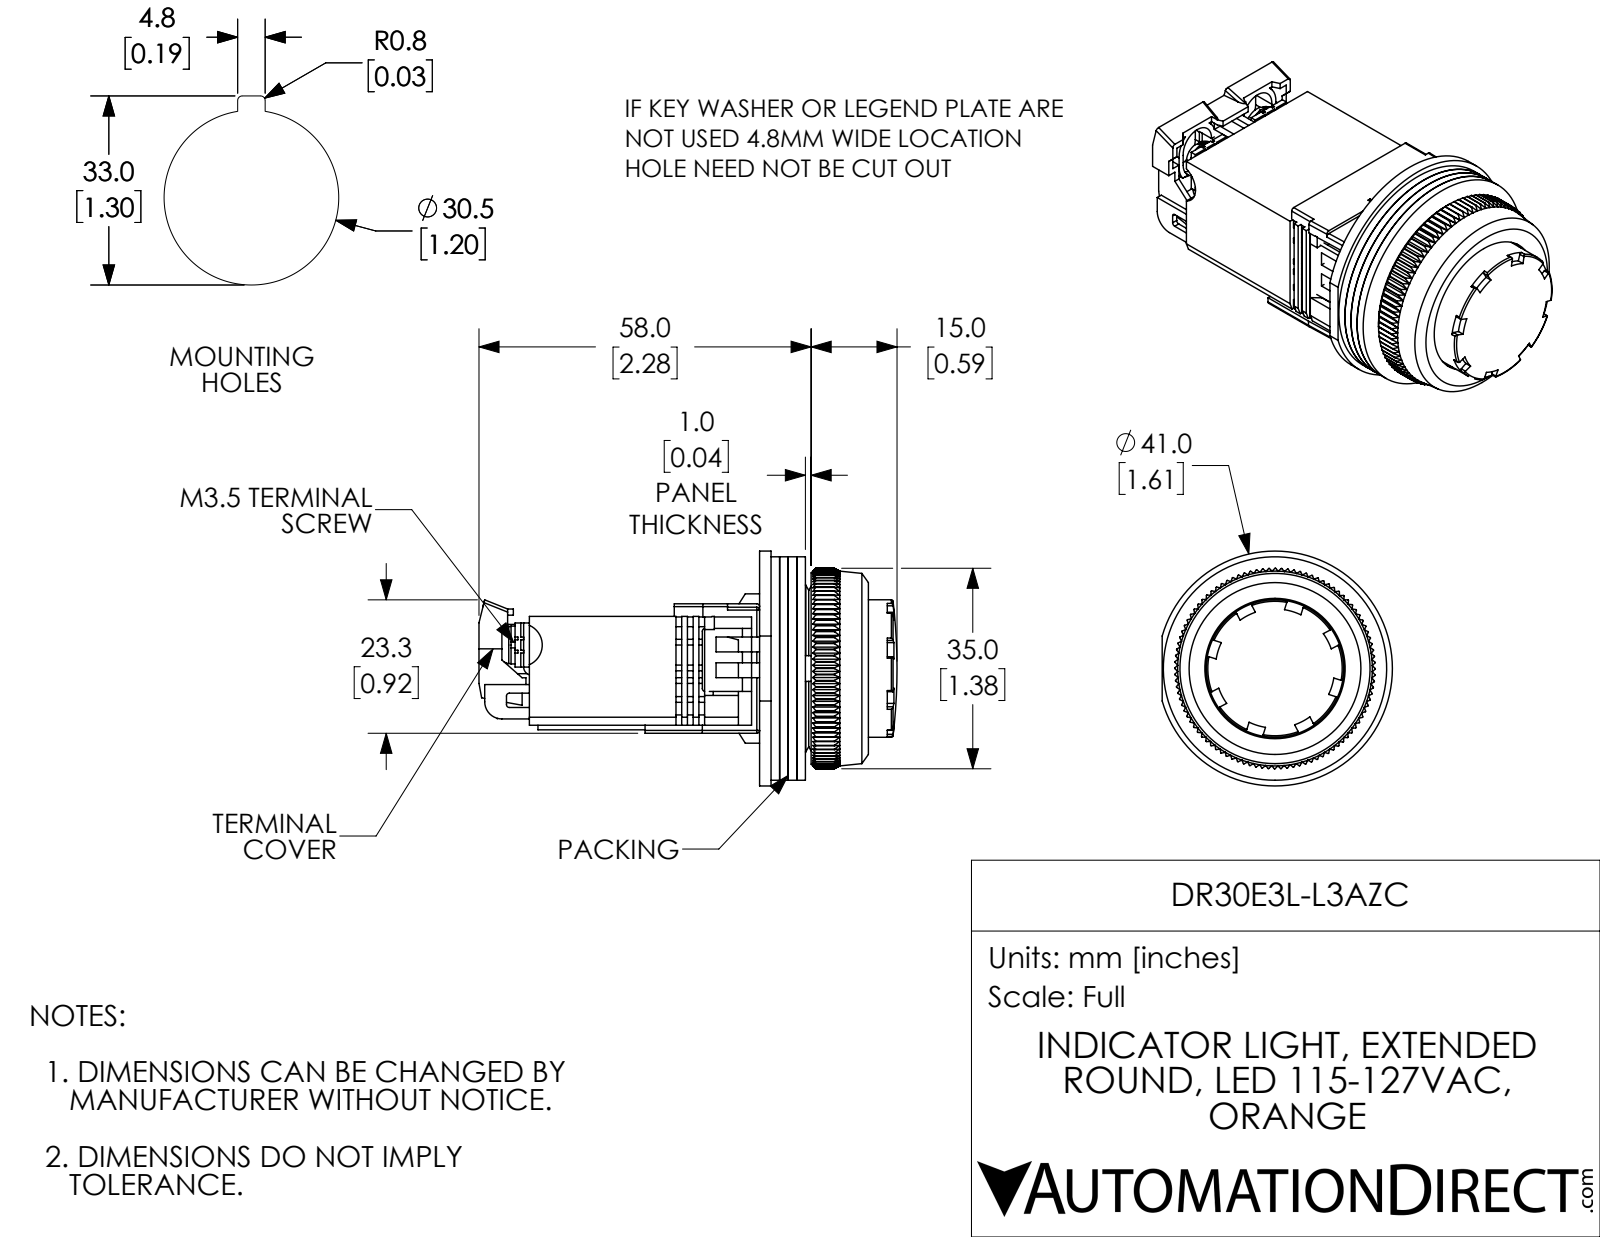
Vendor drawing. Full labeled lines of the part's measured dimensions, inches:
Part name (STEP PRODUCT): DR30E3L-L3AZC
STEP written by: SolidWorks 2017 (AUTOMOTIVE_DESIGN)
Units: inches
Bodies: 19 solids, 1662 faces (1058 planar, 340 cylindrical, 264 other)
Overall size (bounding box): 2.874 × 1.614 × 1.583
Volume: 2.318 in³ · Surface area: 53.06 in²
Round holes (diameter × count): ⌀0.118 ×2, ⌀0.138 ×2, ⌀0.142 ×2, ⌀0.465 ×1, ⌀0.563 ×1, ⌀0.72 ×1, ⌀0.787 ×1, ⌀0.866 ×1, ⌀0.965 ×1, ⌀1.122 ×1, ⌀1.173 ×1, ⌀1.181 ×1
Round bosses / shafts (diameter × count): ⌀0.26 ×2, ⌀0.063 ×2, ⌀1.614 ×1, ⌀1.535 ×1, ⌀1.16 ×1, ⌀0.945 ×1, ⌀0.858 ×1, ⌀0.819 ×1
Partial cylindrical surfaces — rounded edges, fillets, slot ends (radius × count): R0.02 ×24, R0.012 ×16, R0.059 ×9, R0.138 ×2, R0.177 ×2, R0.016 ×1, R0.055 ×1, R0.118 ×1
Main face-to-face distances: 0.059, 0.118, 0.039, 0.177, 0.197, 0.079, 0.256, 0.315, 0.748, 0.138
Hole centre spacings: 0.333, 0.02, 0.324, 0.583, 0.583
